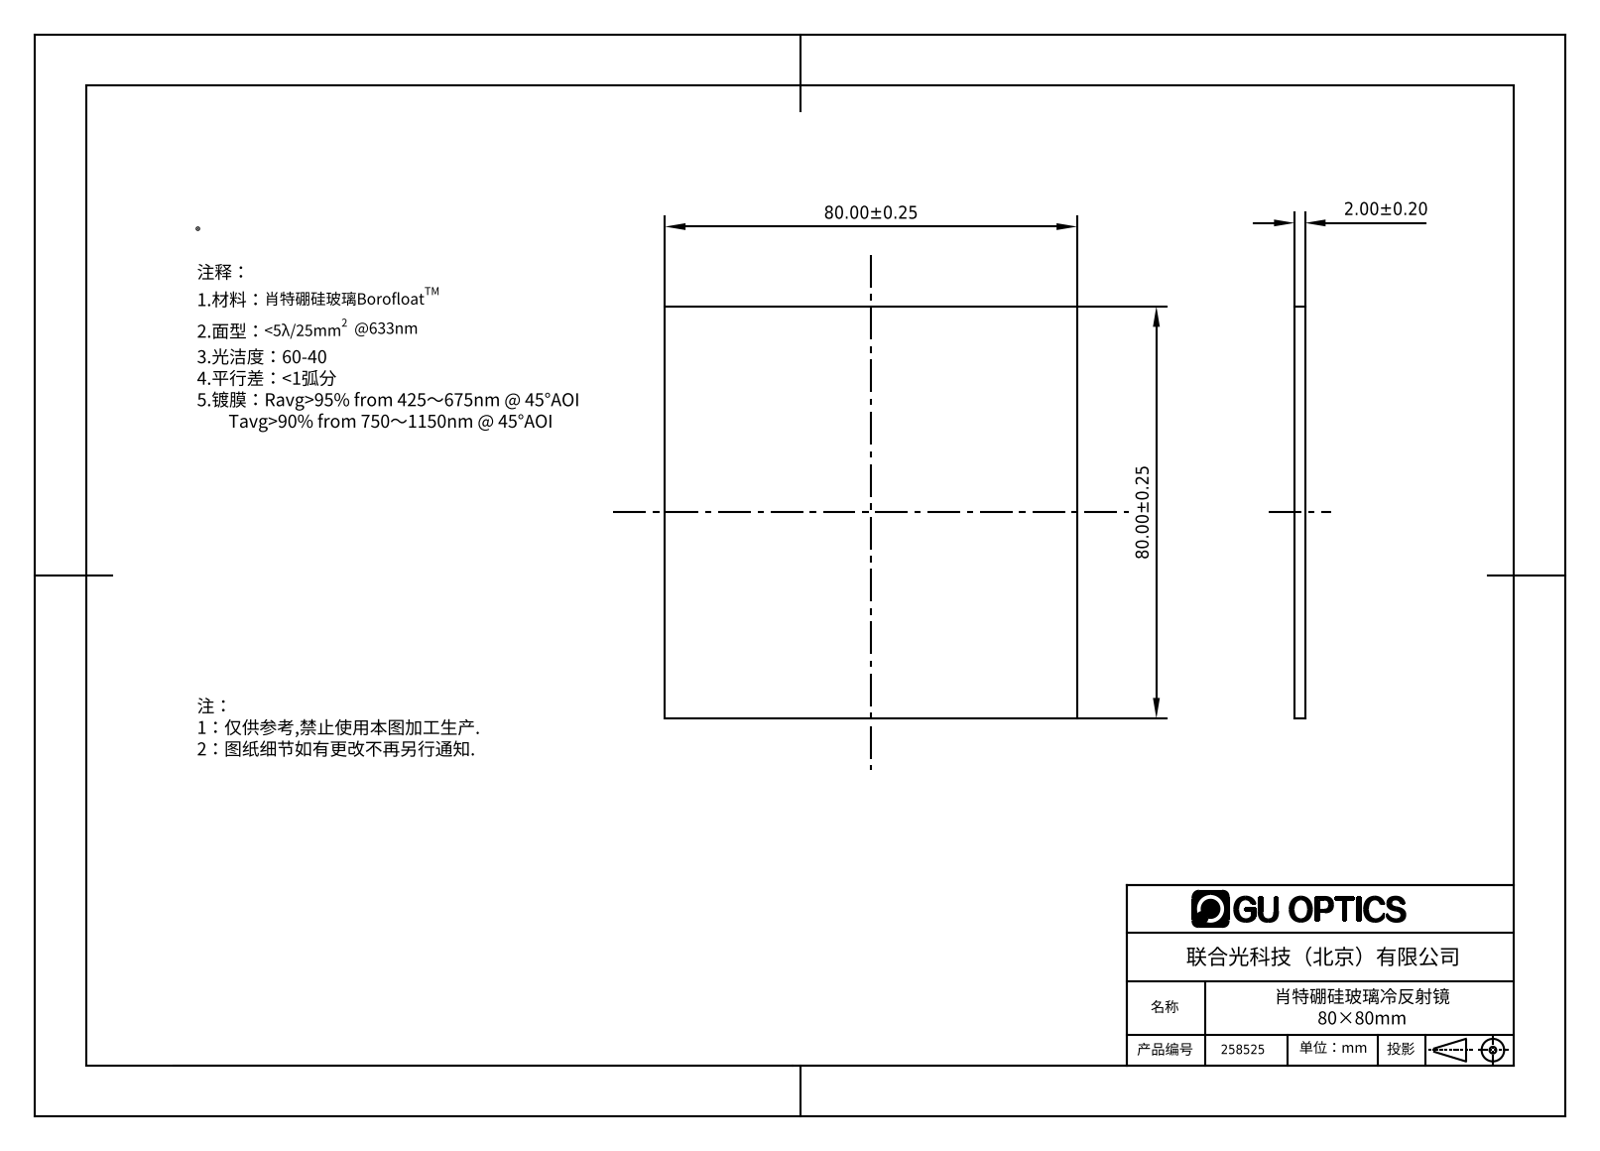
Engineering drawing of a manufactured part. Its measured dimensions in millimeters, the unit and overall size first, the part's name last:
Units: millimetres
Overall size (bounding box): 80 × 80 × 2
Main face-to-face distances: 2, 80
Volume: 12 800 mm³ · Surface area: 13 440 mm²
Bodies: 1 solid, 6 faces (6 planar, 0 cylindrical, 0 other)
Part name (STEP PRODUCT): 258516
STEP written by: SolidWorks 2016 (AUTOMOTIVE_DESIGN)
